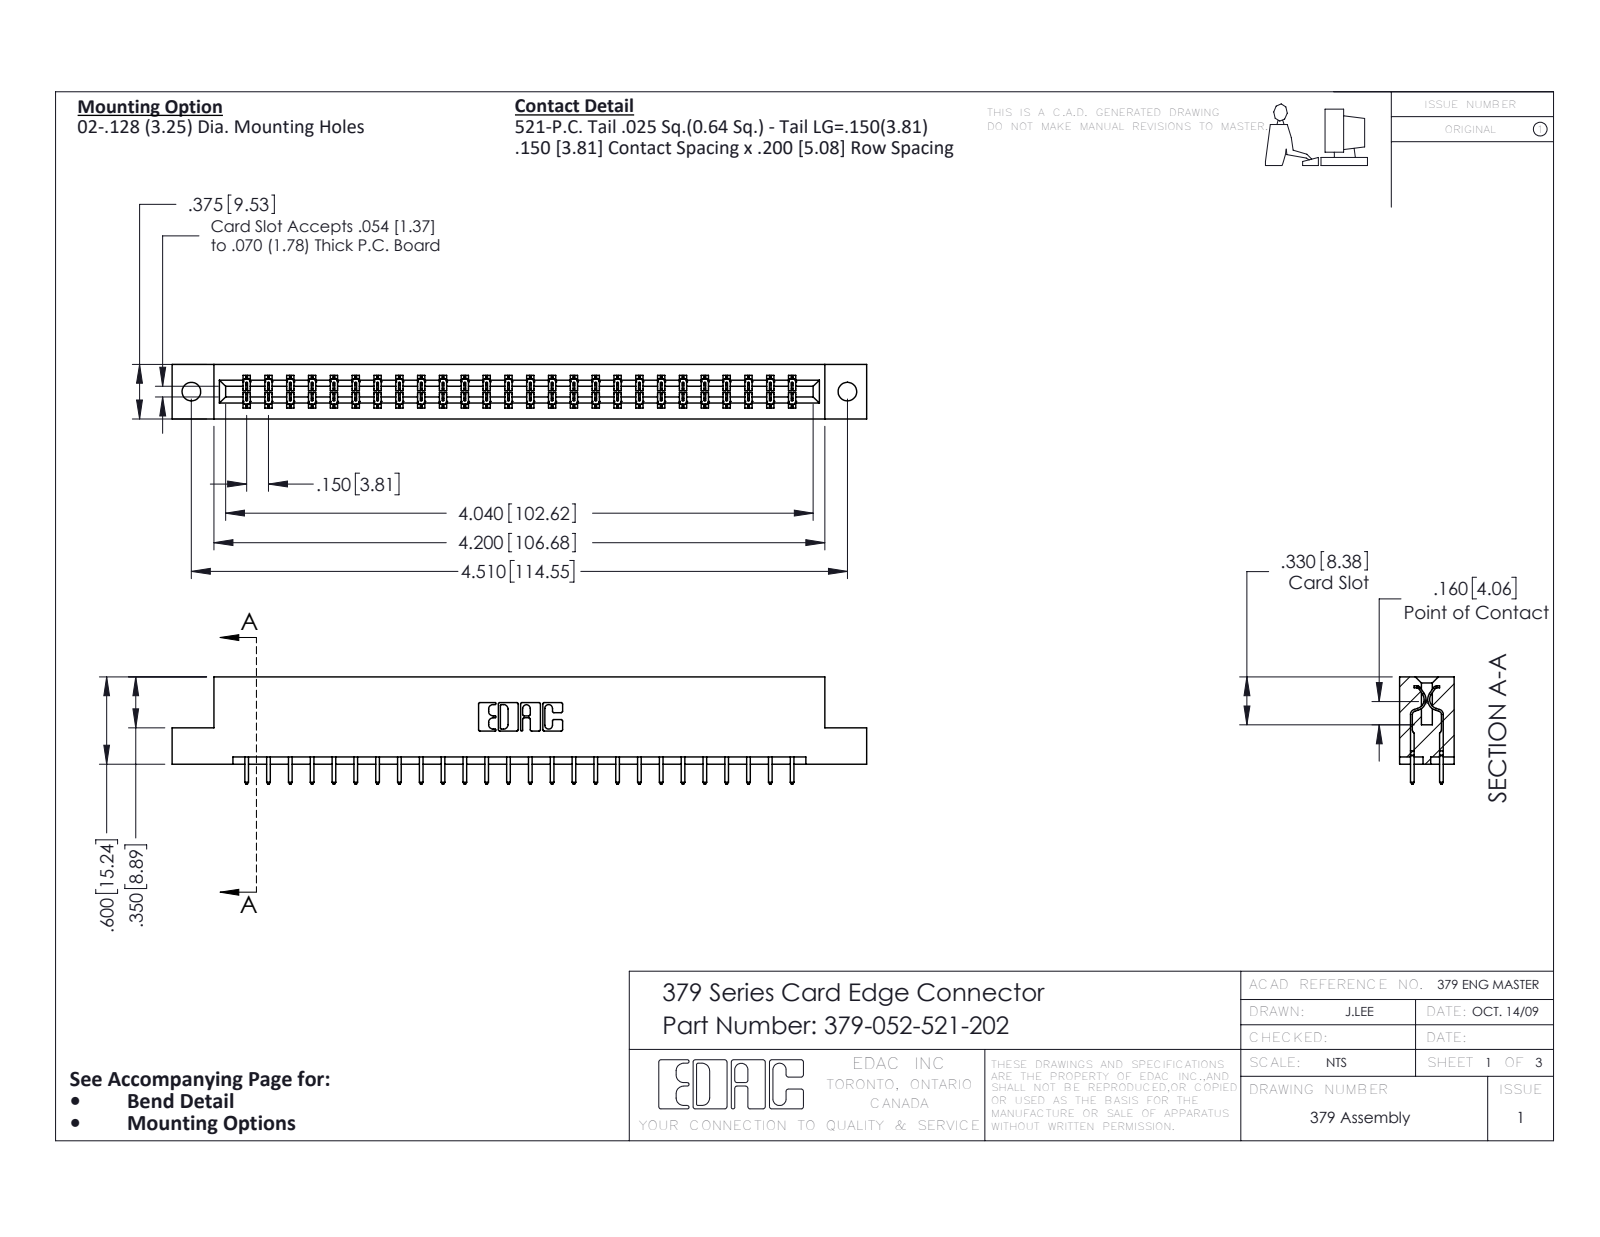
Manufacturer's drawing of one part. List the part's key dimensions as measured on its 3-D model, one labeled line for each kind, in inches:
Part name (STEP PRODUCT): 345-292-001_345-293-121; 379-052-521-202; 379 Part_Flush - .128 Dia
STEP written by: SolidWorks 2016 (CONFIG_CONTROL_DESIGN)
Units: inches
Bodies: 53 solids, 2818 faces (1942 planar, 876 cylindrical, 0 other)
Overall size (bounding box): 4.775 × 0.737 × 0.375
Volume: 0.773 in³ · Surface area: 21.16 in²
Round holes (diameter × count): ⌀0.128 ×2
Partial cylindrical surfaces — rounded edges, fillets, slot ends (radius × count): R0.006 ×78, R0.01 ×52, R0.01 ×22, R0.007 ×6, R0.031 ×6, R0.026 ×3, R0.014 ×2, R0.022 ×2
Main face-to-face distances: 0.3, 0.075, 0.375, 0.2, 0.1, 0.225, 0.076, 0.15, 0.275, 0.55
Hole centre spacings: 4.51
